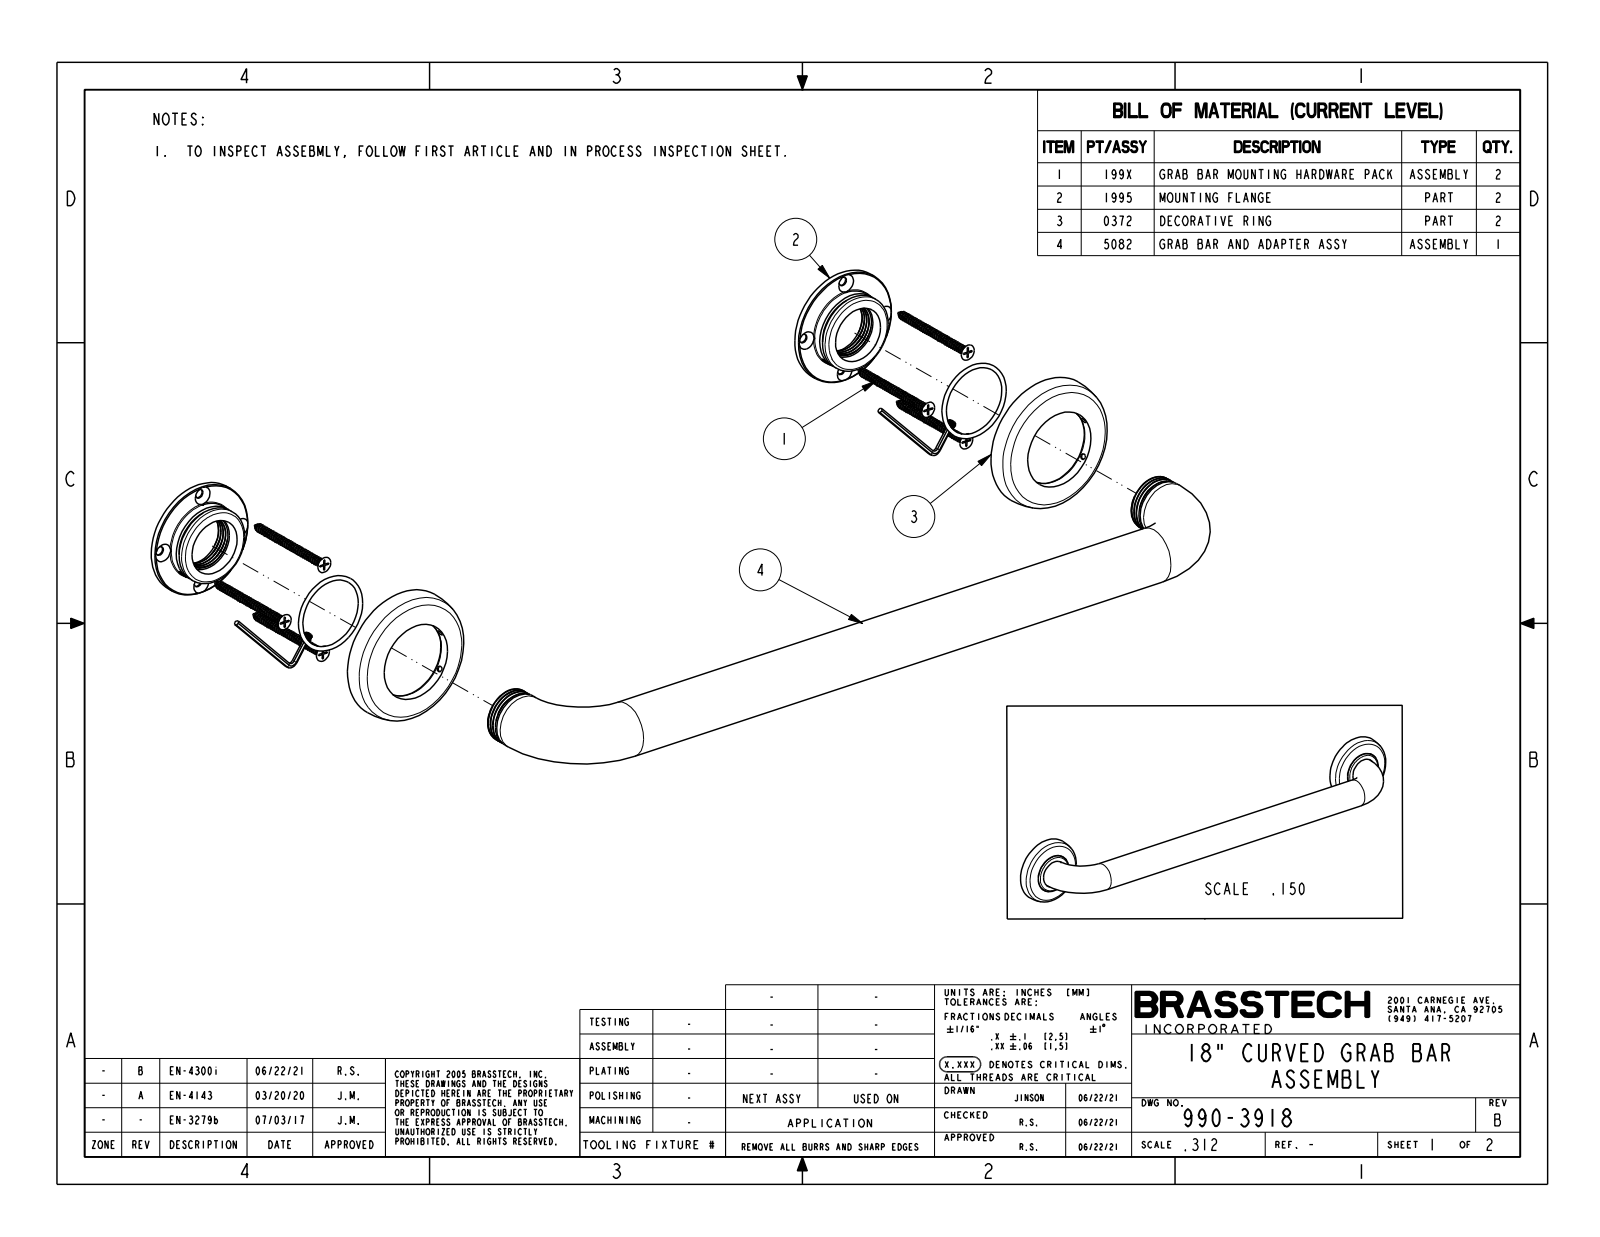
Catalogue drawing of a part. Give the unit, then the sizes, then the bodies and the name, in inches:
Units: inches
Overall size (bounding box): 21 × 3 × 2.912
Round holes (diameter × count): ⌀0.202 ×8, ⌀0.1 ×4, ⌀1.152 ×3, ⌀0.163 ×2, ⌀0.866 ×2, ⌀1.16 ×2, ⌀1.26 ×2, ⌀1.77 ×2
Round bosses / shafts (diameter × count): ⌀1.75 ×4, ⌀0.126 ×4, ⌀1.25 ×3, ⌀2.6 ×2, ⌀1.928 ×2, ⌀1.594 ×2, ⌀1.237 ×2, ⌀1.147 ×2
Partial cylindrical surfaces — rounded edges, fillets, slot ends (radius × count): R0.212 ×8, R0.038 ×4, R0.025 ×2
Main face-to-face distances: 0.15, 0.45, 0.6, 0.074, 0.076, 0.526, 0.1, 0.35, 0.25, 0.05
Hole centre spacings: 1.087, 1.538, 18, 2.175, 16.948, 18.033, 19.119, 0.084
Volume: 7.914 in³ · Surface area: 347.5 in²
Bodies: 7 solids, 752 faces (228 planar, 200 cylindrical, 324 other)
Part name (STEP PRODUCT): 1995; 20-287_ASM; 80528; 50869 (+3 more)
STEP written by: PRO/ENGINEER BY PARAMETRIC TECHNOLOGY CORPORATION, 2013150 (CONFIG_CONTROL_DESIGN)
